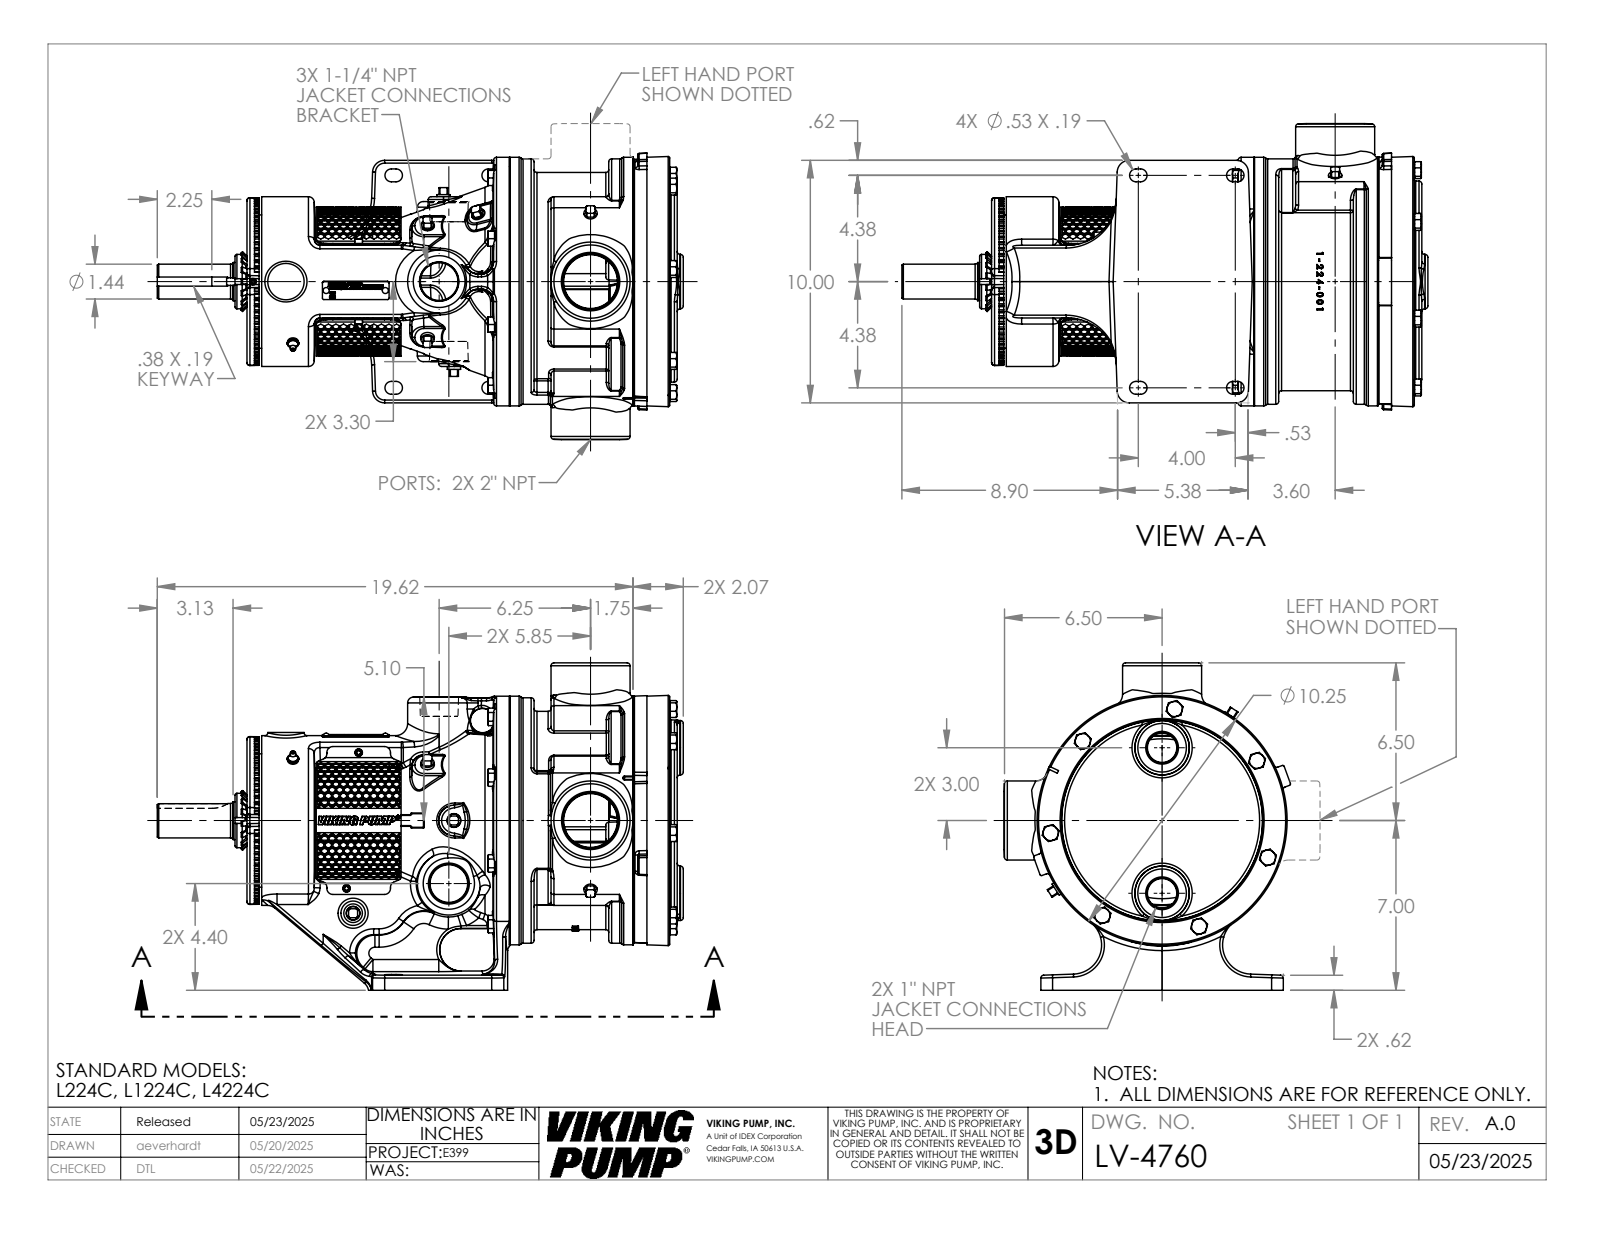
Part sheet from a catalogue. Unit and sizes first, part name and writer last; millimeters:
Units: millimetres
Overall size (bounding box): 551.1 × 342.9 × 300
Round holes (diameter × count): ⌀27.8 ×8, ⌀5.1 ×6, ⌀6.4 ×6, ⌀4 ×3, ⌀6.8 ×2, ⌀8 ×2, ⌀11.5 ×1, ⌀40.1 ×1, ⌀40.5 ×1, ⌀46.5 ×1, ⌀62 ×1, ⌀133.4 ×1
Round bosses / shafts (diameter × count): ⌀15.9 ×9, ⌀15.9 ×6, ⌀11.1 ×3, ⌀7.9 ×3, ⌀82.8 ×2, ⌀260.4 ×1, ⌀257 ×1, ⌀177.8 ×1
Partial cylindrical surfaces — rounded edges, fillets, slot ends (radius × count): R1.6 ×109, R1.8 ×74, R3 ×66, R12.7 ×26, R6.1 ×16, R1.5 ×14, R0.8 ×12, R6.4 ×12
Main face-to-face distances: 7.9, 12.7, 373, 380.9, 57.2, 89.8, 283.2, 291.1, 54.4, 144.3
Hole centre spacings: 76.2, 34.9, 55.4, 91.7, 112.9, 117.5, 162.7, 166.1
Volume: 15 640 000 mm³ · Surface area: 761 300 mm²
Bodies: 1 solid, 4013 faces (1307 planar, 753 cylindrical, 1953 other)
Part name (STEP PRODUCT): LV-4760
STEP written by: SolidWorks 2024 (AUTOMOTIVE_DESIGN)
